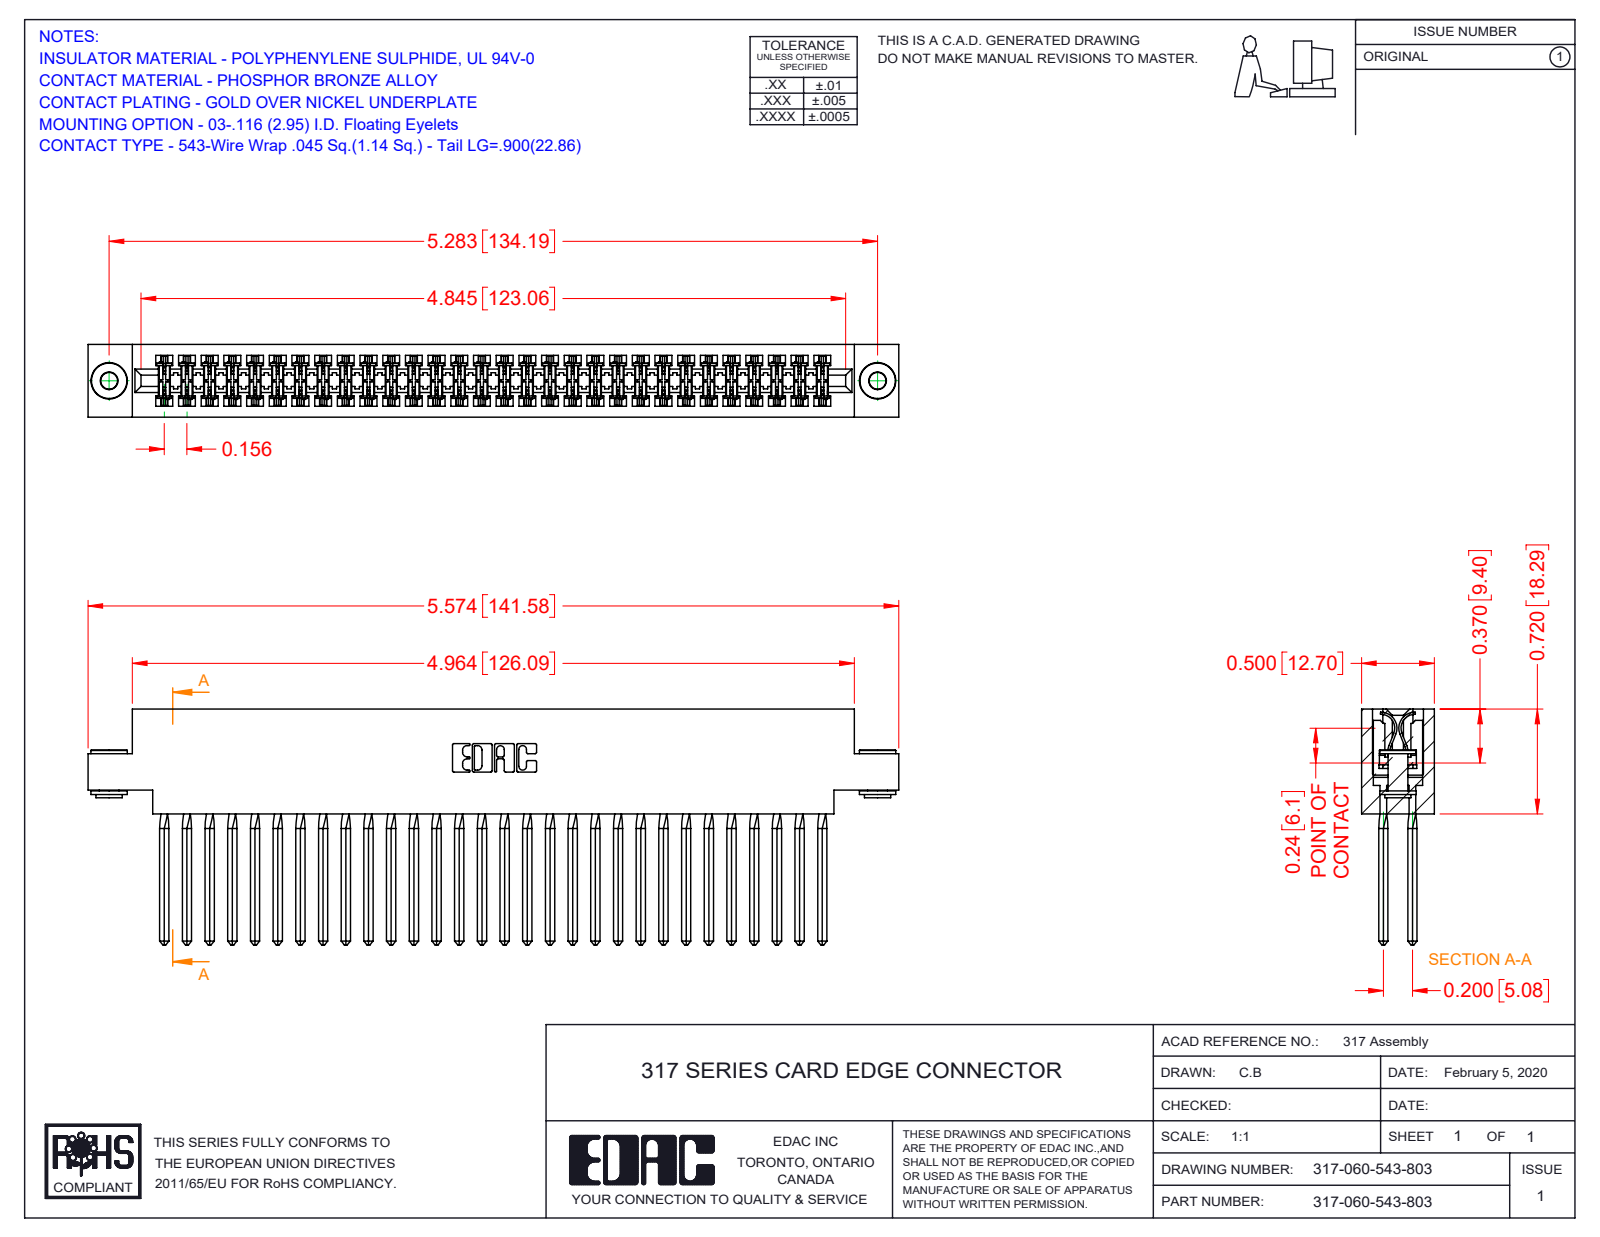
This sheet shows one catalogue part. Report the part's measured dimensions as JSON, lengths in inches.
{"part_name": "317-290-001_543; 317 Part_.156 Dia - TH; 345-250-002_345-250-002-102; 317-060-543-803", "step_written_by": "SolidWorks 2016 (CONFIG_CONTROL_DESIGN)", "units": "inches", "bodies": {"solids": 63, "faces": 5480, "planar": 4448, "cylindrical": 784, "other": 248}, "overall_size": [5.574, 1.62, 0.5], "volume_in3": 1.445, "surface_area_in2": 55.27, "round_holes": [[0.116, 2], [0.156, 2]], "round_bosses_or_shafts": [[0.25, 2], [0.18, 2], [0.136, 2]], "partial_cylinders_radius": [[0.015, 120], [0.01, 22], [0.007, 6], [0.031, 6], [0.026, 3], [0.095, 2], [0.1, 2], [0.11, 2]], "face_to_face_distances": [0.5, 0.075, 0.425, 0.35, 0.11, 0.195, 0.094, 0.2, 0.72, 0.115], "hole_center_spacings": [5.283]}
